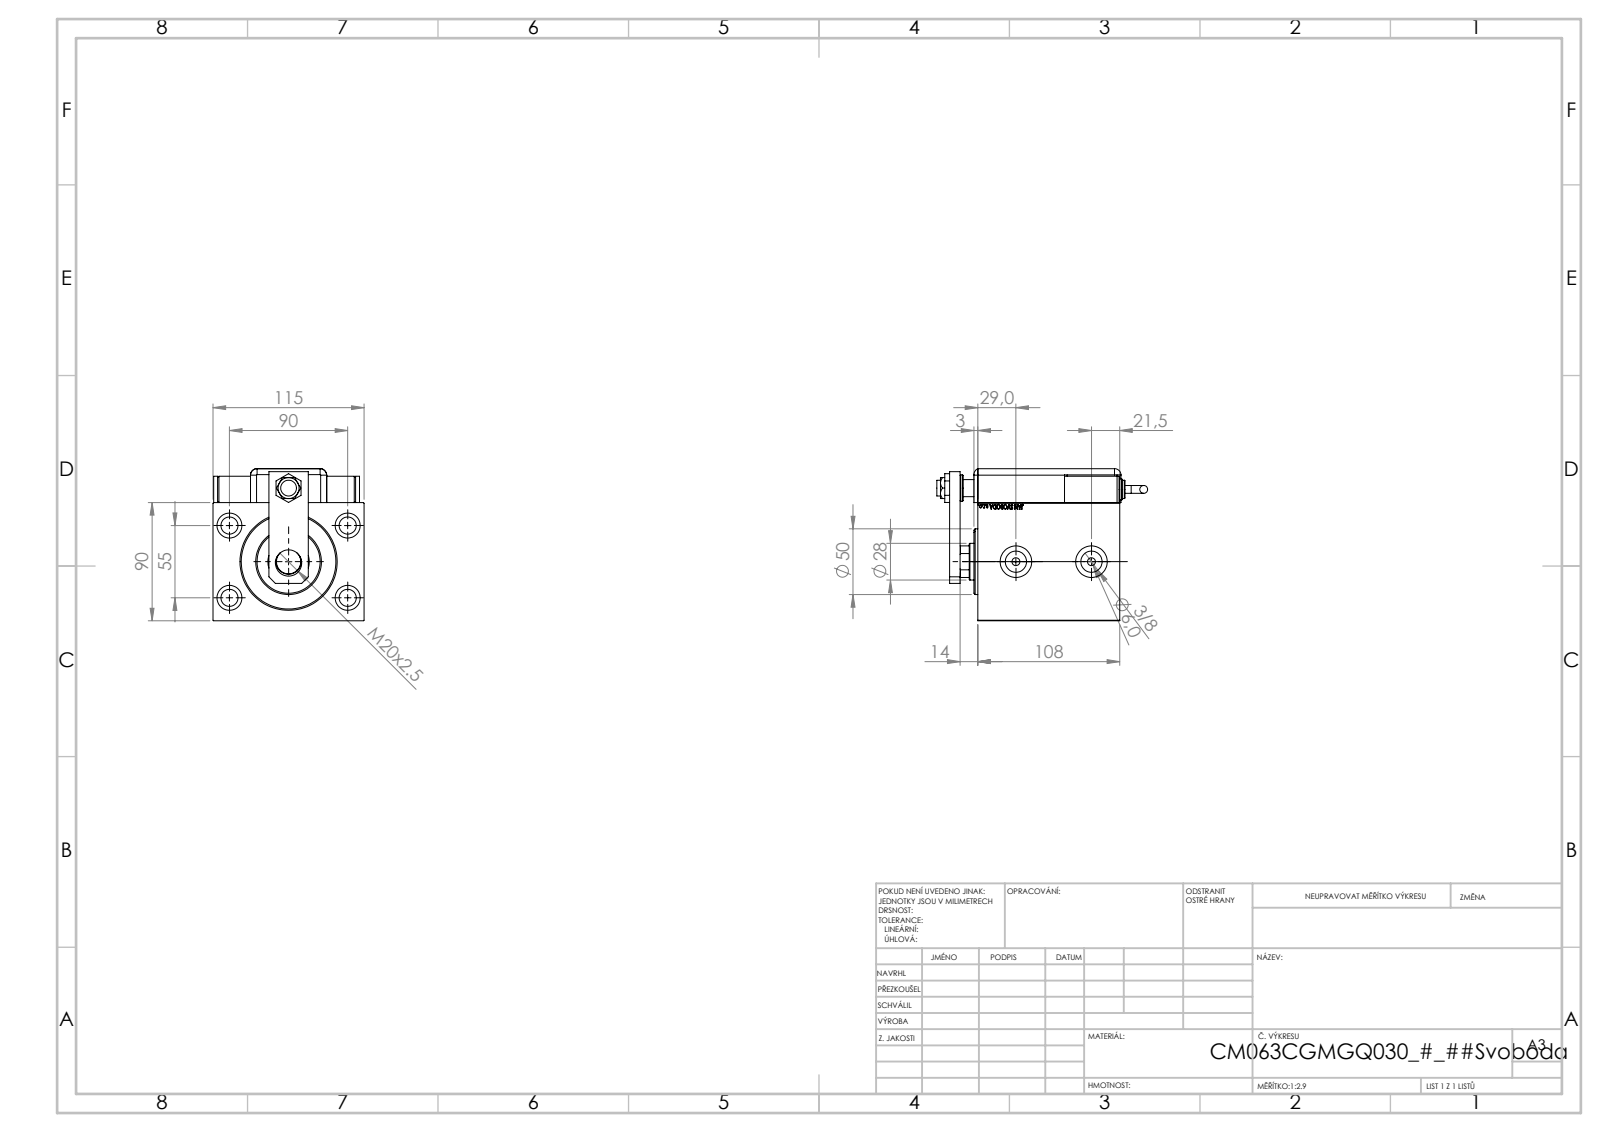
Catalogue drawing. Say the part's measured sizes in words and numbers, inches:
The part is named "SWITCH_Q_FRONT_BACK; ZARAZKA_Q; SWITCH DIM A_G; V450CM_C_VCP (+7 more)". Its 3-D file was written by "SolidWorks 2019 (CONFIG_CONTROL_DESIGN)". It is 13 solids with 1249 faces: 615 planar, 117 cylindrical and 517 other. Overall it measures 6.317 by 4.559 by 4.528 inches. Its volume is 68.1 cubic inches and its surface area 301 square inches. Round holes: 5 of diameter 0.512, 4 of diameter 0.748, 2 of diameter 0.157, 2 of diameter 0.236, 2 of diameter 0.315, 2 of diameter 0.637, 2 of diameter 0.945, 1 of diameter 0.472, 1 of diameter 0.551, 1 of diameter 0.728, 1 of diameter 0.787, 1 of diameter 1.102. Round bosses or shafts: 3 of diameter 0.787, 2 of diameter 0.63, 2 of diameter 0.551, 2 of diameter 0.236, 1 of diameter 1.969. Partial cylindrical surfaces (rounded edges, fillets, slot ends): 9 of radius 0.197, 1 of radius 0.394, 1 of radius 0.531. The main face-to-face distances are 3.543, 0.118, 4.252, 4.528, 3.563, 0.689, 0.531, 0.315, 1.016, 4.559. The hole center spacings are 2.076, 2.097, 2.056, 2.165, 3.543, 3.734, 4.153, 0.039.
